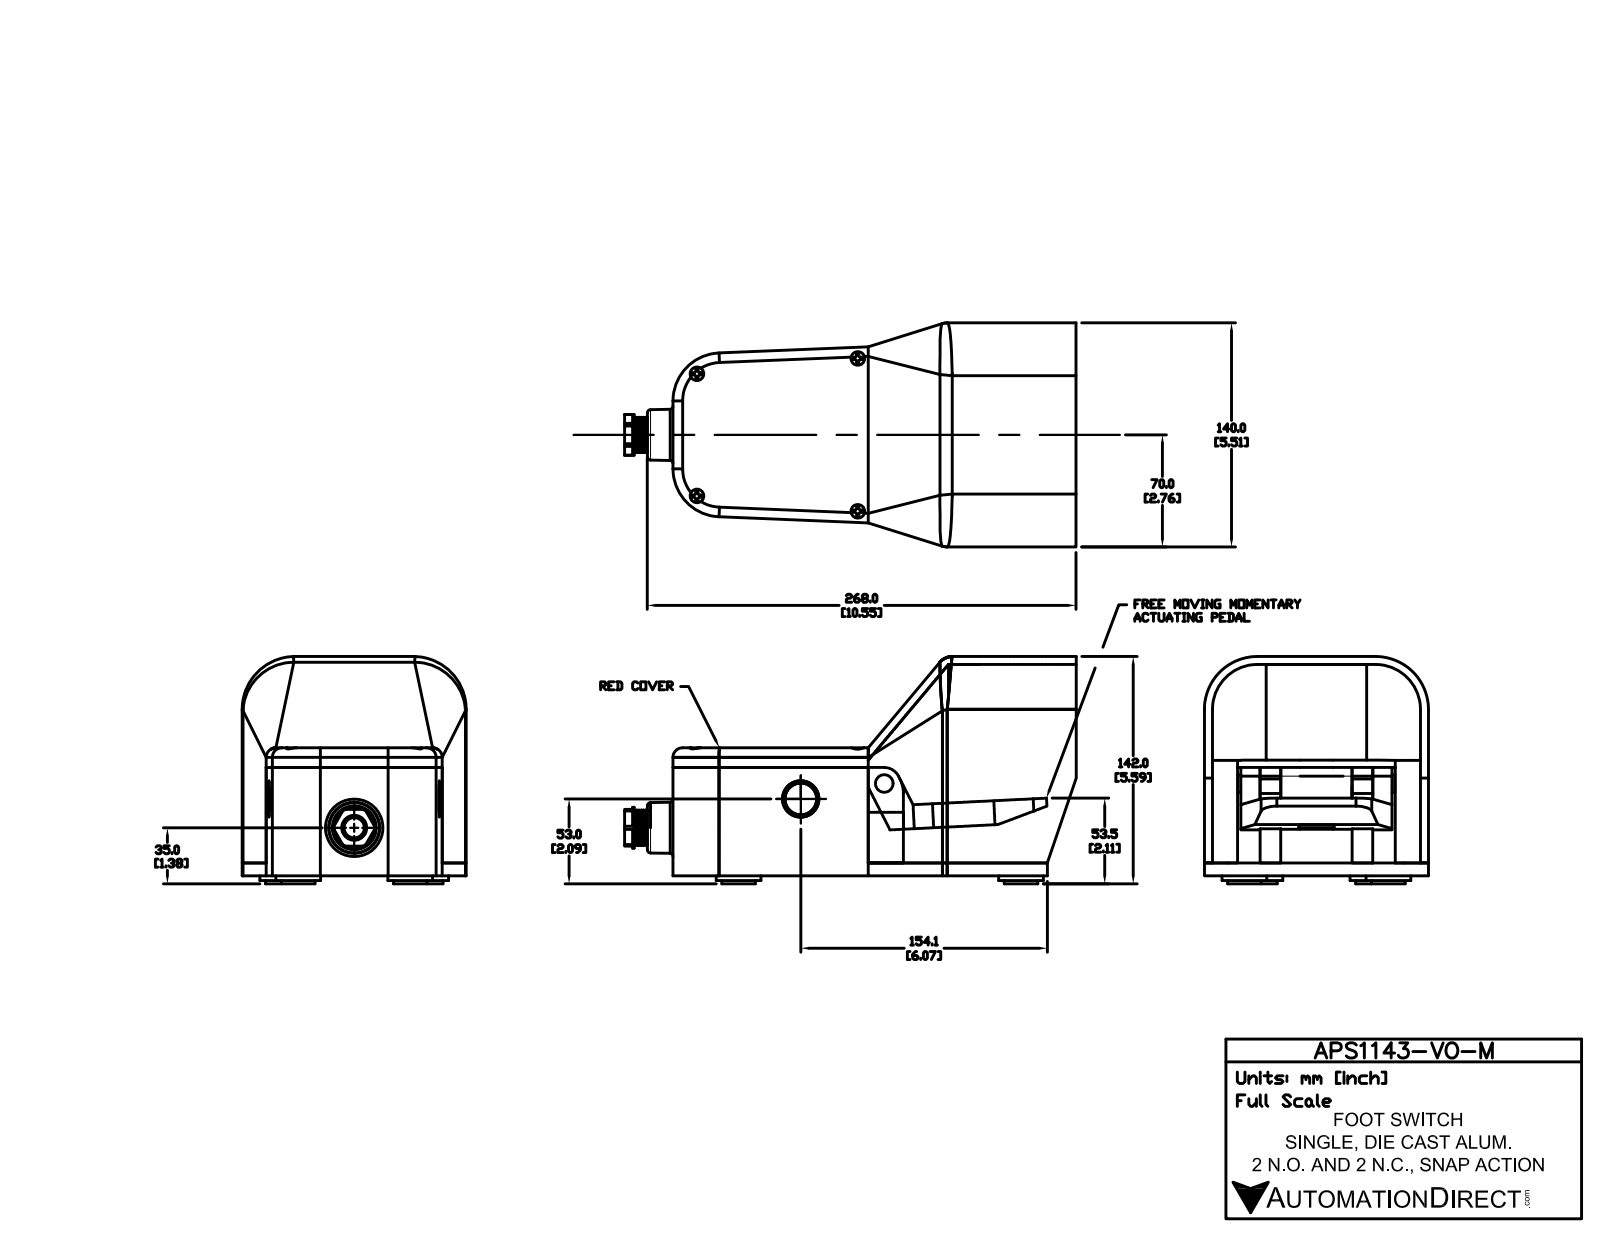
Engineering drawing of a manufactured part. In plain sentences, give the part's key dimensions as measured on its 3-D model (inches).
The part is named "APS1143-V0-M". Its 3-D file was written by "SolidWorks 2015 (AUTOMOTIVE_DESIGN)". It is 18 solids with 361 faces: 214 planar, 91 cylindrical and 56 other. Overall it measures 11.112 by 5.591 by 5.512 inches. Its volume is 94.04 cubic inches and its surface area 415.4 square inches. Round holes: 4 of diameter 0.335, 2 of diameter 0.896, 1 of diameter 0.498, 1 of diameter 0.614. Round bosses or shafts: 4 of diameter 1.102, 4 of diameter 0.827, 2 of diameter 0.782, 1 of diameter 1.004, 1 of diameter 0.866, 1 of diameter 0.433. Partial cylindrical surfaces (rounded edges, fillets, slot ends): 16 of radius 0.039, 6 of radius 0.394, 3 of radius 0.236, 2 of radius 1.102, 2 of radius 1.181, 2 of radius 1.299, 1 of radius 0.787. The main face-to-face distances are 0.197, 5.315, 0.315, 2.348, 2.664, 2.349, 2.663, 5.512, 3.15, 2.835. The hole center spacings are 3.976, 5.206, 3.004, 3.76.
